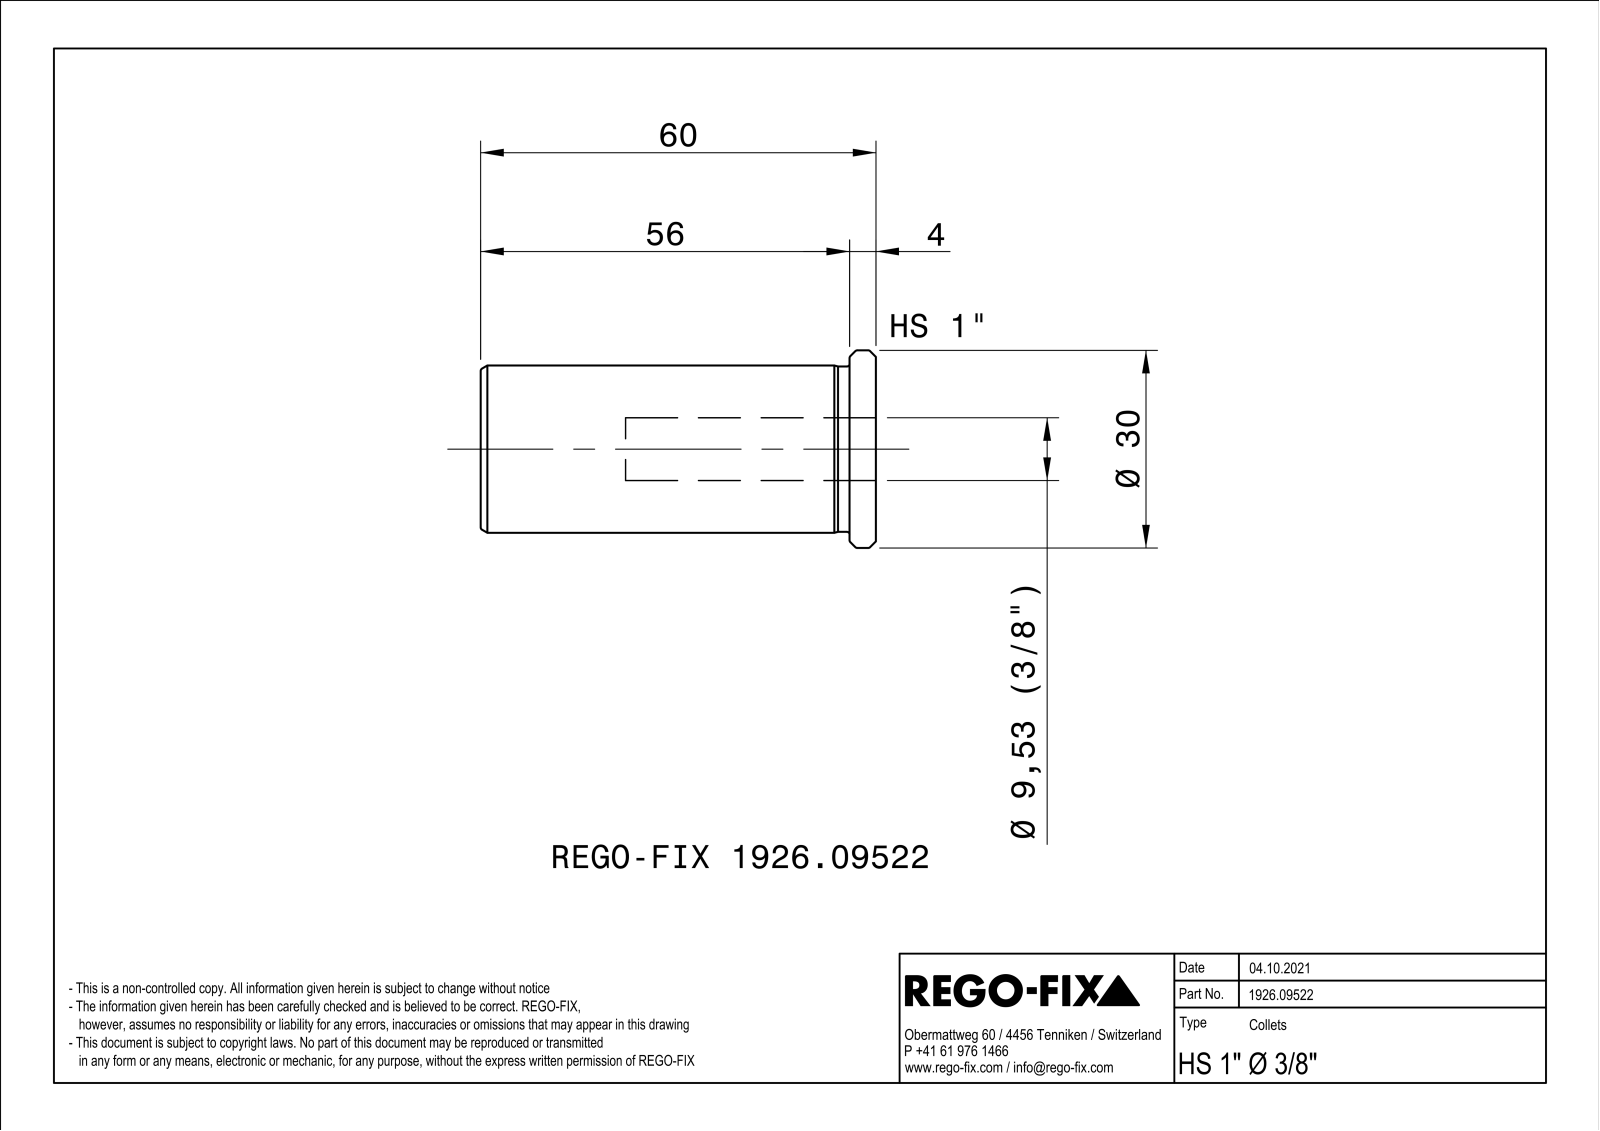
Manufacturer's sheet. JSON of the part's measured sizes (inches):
{"part_name": "NOCUT", "step_written_by": "SIEMENS PLM Software Solid Edge ST10 (AUTOMOTIVE_DESIGN)", "units": "inches", "bodies": {"solids": 1, "faces": 72, "planar": 22, "cylindrical": 12, "other": 38}, "overall_size": [2.362, 1.18, 1.18], "volume_in3": 1.366, "surface_area_in2": 15.62, "round_holes": [[0.375, 1], [0.394, 1], [0.807, 1]], "round_bosses_or_shafts": [[1.181, 1], [1, 1], [0.988, 1]], "face_to_face_distances": [0.039, 2.362, 0.157, 2.205]}
